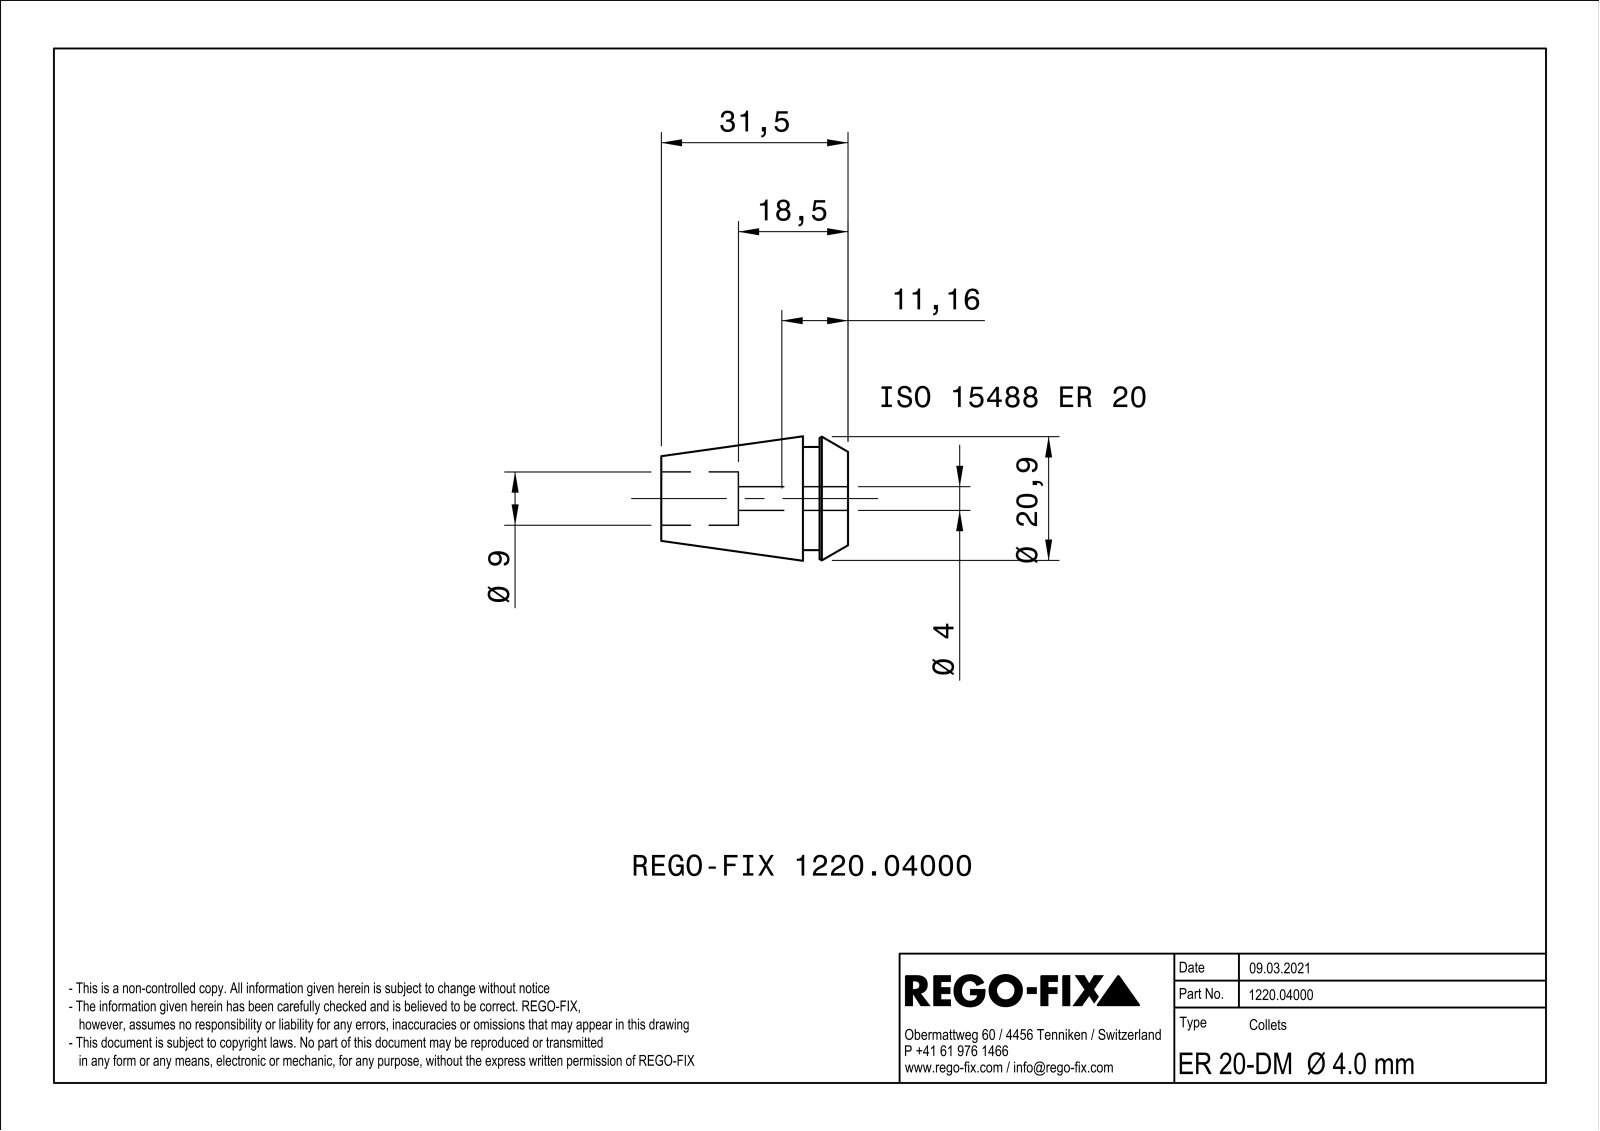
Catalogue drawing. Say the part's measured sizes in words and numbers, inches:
The part is named "NOCUT". Its 3-D file was written by "SIEMENS PLM Software Solid Edge ST10 (AUTOMOTIVE_DESIGN)". It is 1 solid with 94 faces: 44 planar, 9 cylindrical and 41 other. Overall it measures 1.24 by 0.811 by 0.811 inches. Its volume is 0.35 cubic inches and its surface area 6.718 square inches. Round holes: 1 of diameter 0.157, 1 of diameter 0.354. Round bosses or shafts: 1 of diameter 0.685. The main face-to-face distances are 0.02, 0.299, 0.189, 0.11, 1.24, 1.051, 0.941, 0.728, 0.539, 0.429.
